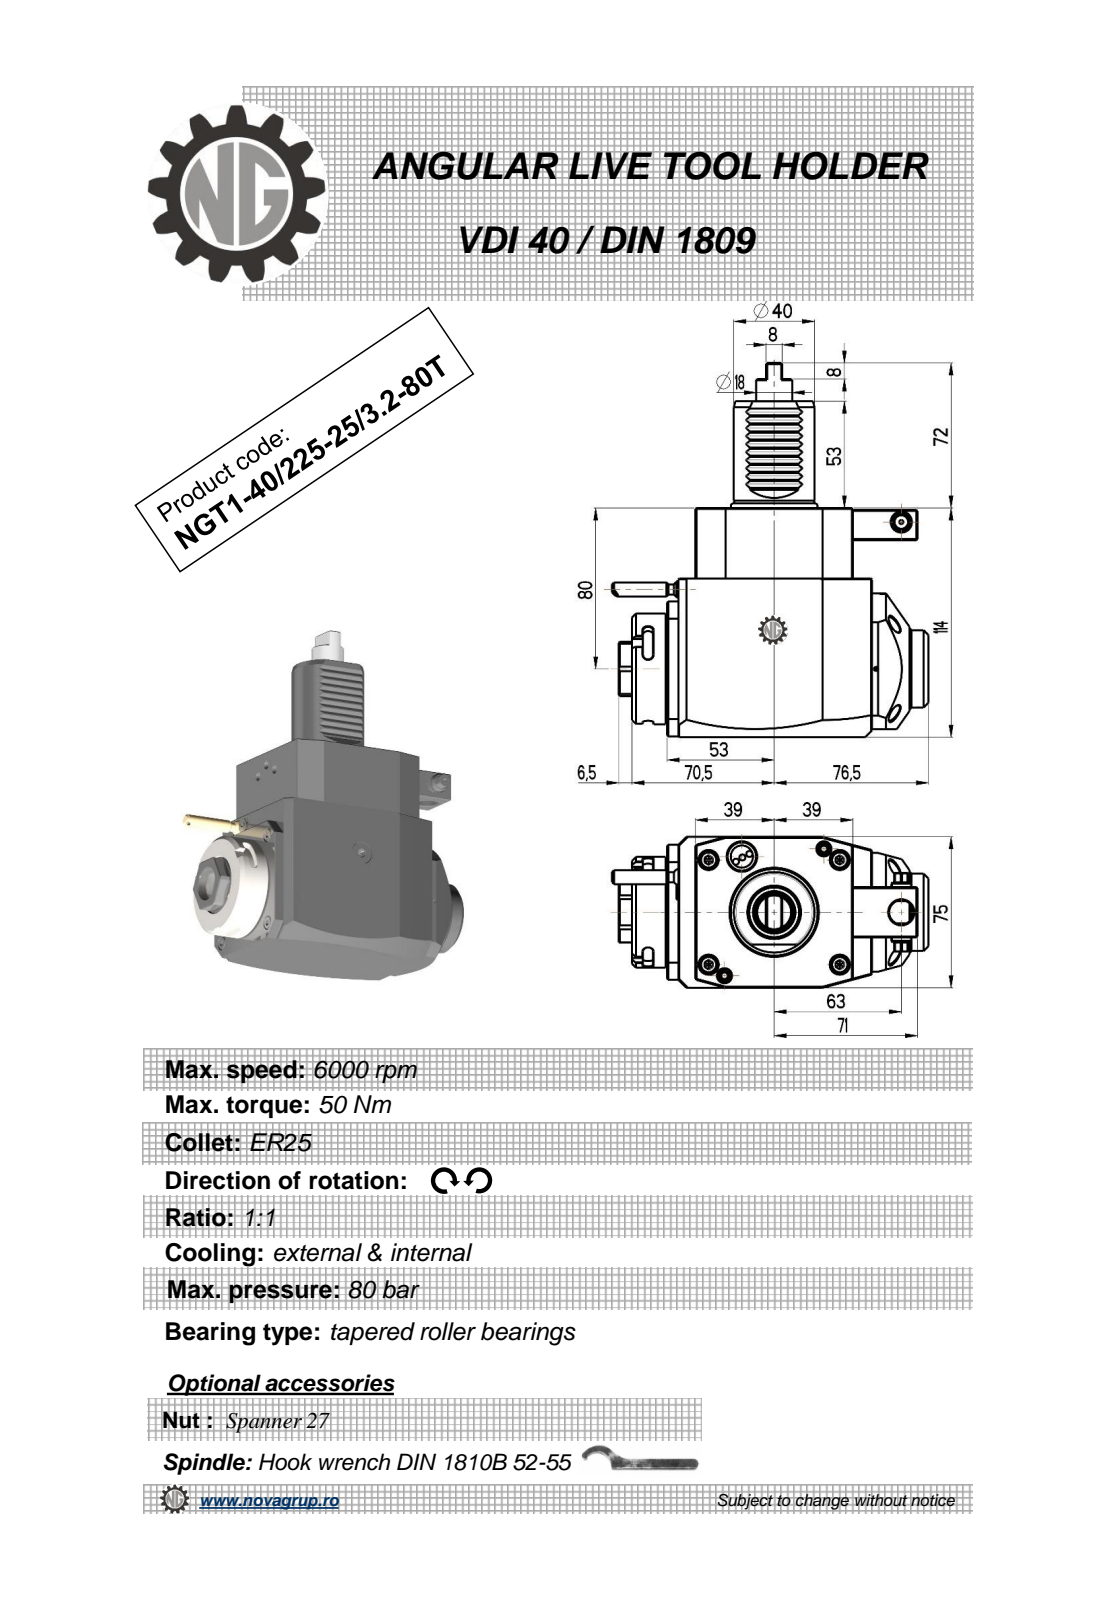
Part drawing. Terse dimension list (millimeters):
name: NGT1_40_225_25_3_2_80T
written by: PRO/ENGINEER BY PARAMETRIC TECHNOLOGY CORPORATION, 2010280 (CONFIG_CONTROL_DESIGN)
unit: mm
bodies: 1 solid, 348 faces (186 planar, 88 cylindrical, 74 other)
size: 186 × 156.83 × 75
volume: 960 012 mm³; area: 71 379 mm²
holes: 1× ⌀2, 1× ⌀2.5, 1× ⌀3, 1× ⌀9.5, 1× ⌀12, 1× ⌀18
bosses: 2× ⌀8, 1× ⌀55, 1× ⌀48, 1× ⌀40, 1× ⌀38.5, 1× ⌀17.8, 1× ⌀10, 1× ⌀7
rounds: 10× R0.3, 6× R2.5, 2× R0.8, 2× R180, 1× R0.5, 1× R3.85, 1× R4.25, 1× R15
face distances: 75, 114, 14, 17.5, 92, 78, 31.5, 109.5, 35, 4
hole spacings: 37.35, 43.2, 72.5
